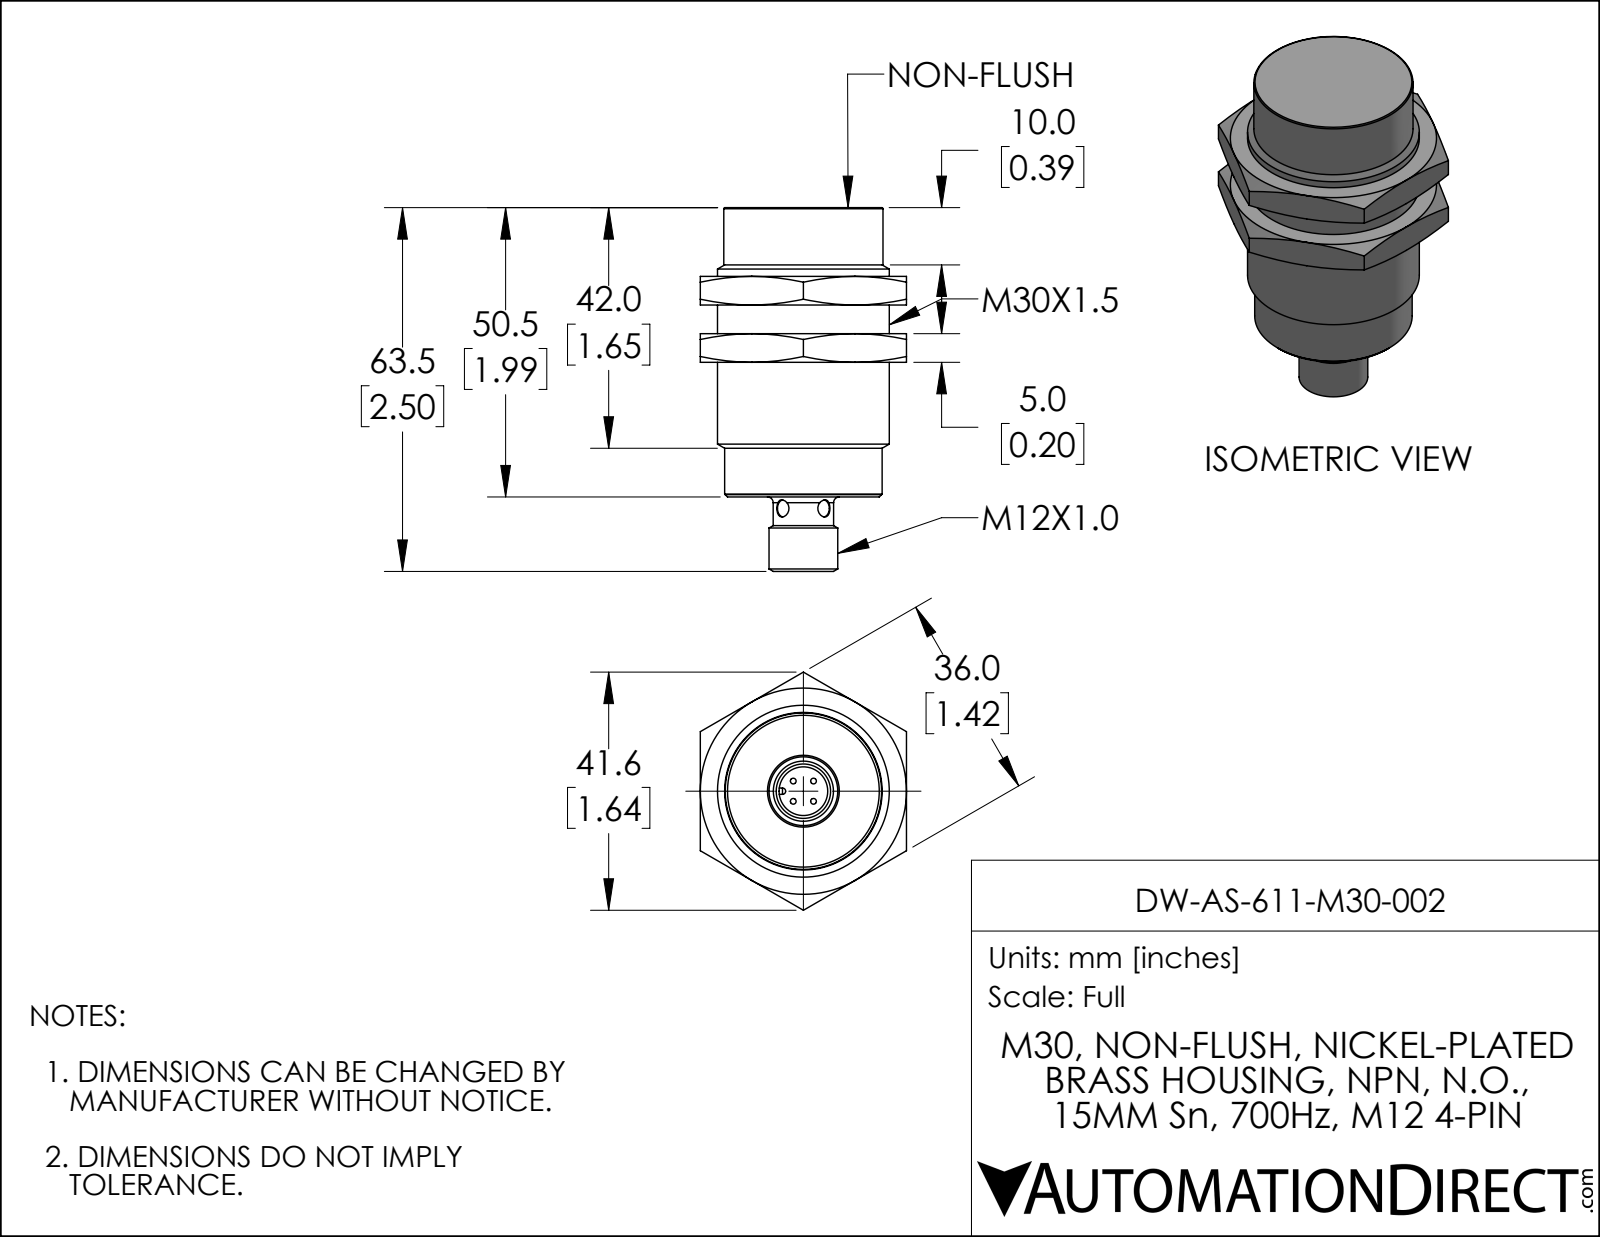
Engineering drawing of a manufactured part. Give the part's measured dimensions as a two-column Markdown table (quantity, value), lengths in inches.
| quantity | value |
| --- | --- |
| part name | DW-AS-611-M30-002 |
| STEP written by | SolidWorks 2019 (AUTOMOTIVE_DESIGN) |
| units | inches |
| bodies | 1 solid, 84 faces (28 planar, 19 cylindrical, 37 other) |
| overall size | 2.5 × 1.637 × 1.417 |
| volume | 2.351 in³ |
| surface area | 13.28 in² |
| round holes (diameter × count) | 0.118 × 2, 0.335 × 1 |
| round bosses / shafts (diameter × count) | 0.039 × 4, 1.181 × 1, 1.094 × 1, 1.083 × 1, 1.075 × 1, 0.472 × 1, 0.415 × 1 |
| partial cylindrical surfaces (radius × count) | 0.022 × 2 |
| main face-to-face distances | 0.197, 0.394, 1.417, 1.988, 0.472, 0.669, 1.516, 0.866, 1.122, 1.063 |
